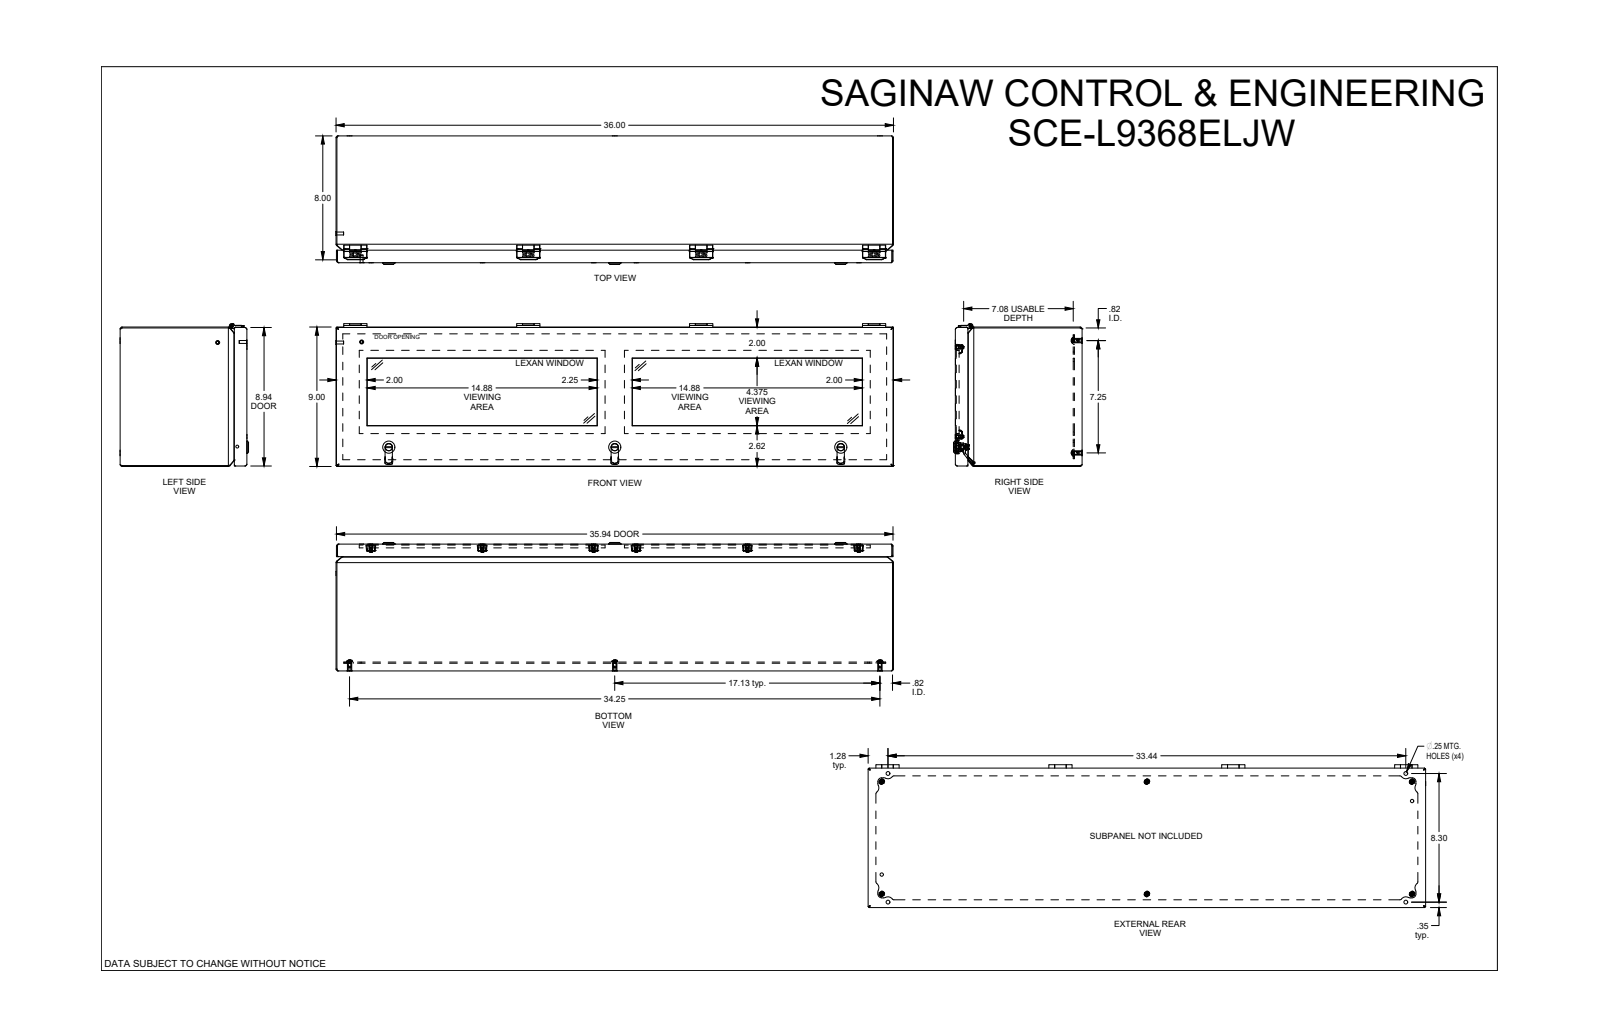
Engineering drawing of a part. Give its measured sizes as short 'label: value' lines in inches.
name: SCE-L9368ELJWSS
written by: SolidWorks 2022 (AUTOMOTIVE_DESIGN)
unit: in
bodies: 94 solids, 3283 faces (1632 planar, 873 cylindrical, 778 other)
size: 36.004 × 9.22 × 8.296
volume: 145.2 in³; area: 3 723 in²
holes: 12× ⌀0.138, 12× ⌀0.156, 12× ⌀0.213, 6× ⌀0.19, 6× ⌀0.25, 6× ⌀0.284, 4× ⌀0.164, 4× ⌀0.174, 4× ⌀0.266, 4× ⌀0.338, 3× ⌀0.2, 3× ⌀0.239
bosses: 12× ⌀0.262, 12× ⌀0.212, 8× ⌀0.188, 6× ⌀0.373, 6× ⌀0.28, 4× ⌀0.26, 4× ⌀0.15, 3× ⌀0.788
rounds: 64× R0.008, 58× R0.02, 54× R0.05, 18× R0.01, 13× R0.25, 11× R0.102, 11× R0.125, 10× R0.06
face distances: 0.059, 8.941, 0.075, 0.571, 0.512, 0.496, 0.437, 8.125, 8.066, 7.629
hole spacings: 17.125, 11.167, 22.333, 8.627, 15.785, 5.77, 7.187, 9.217
